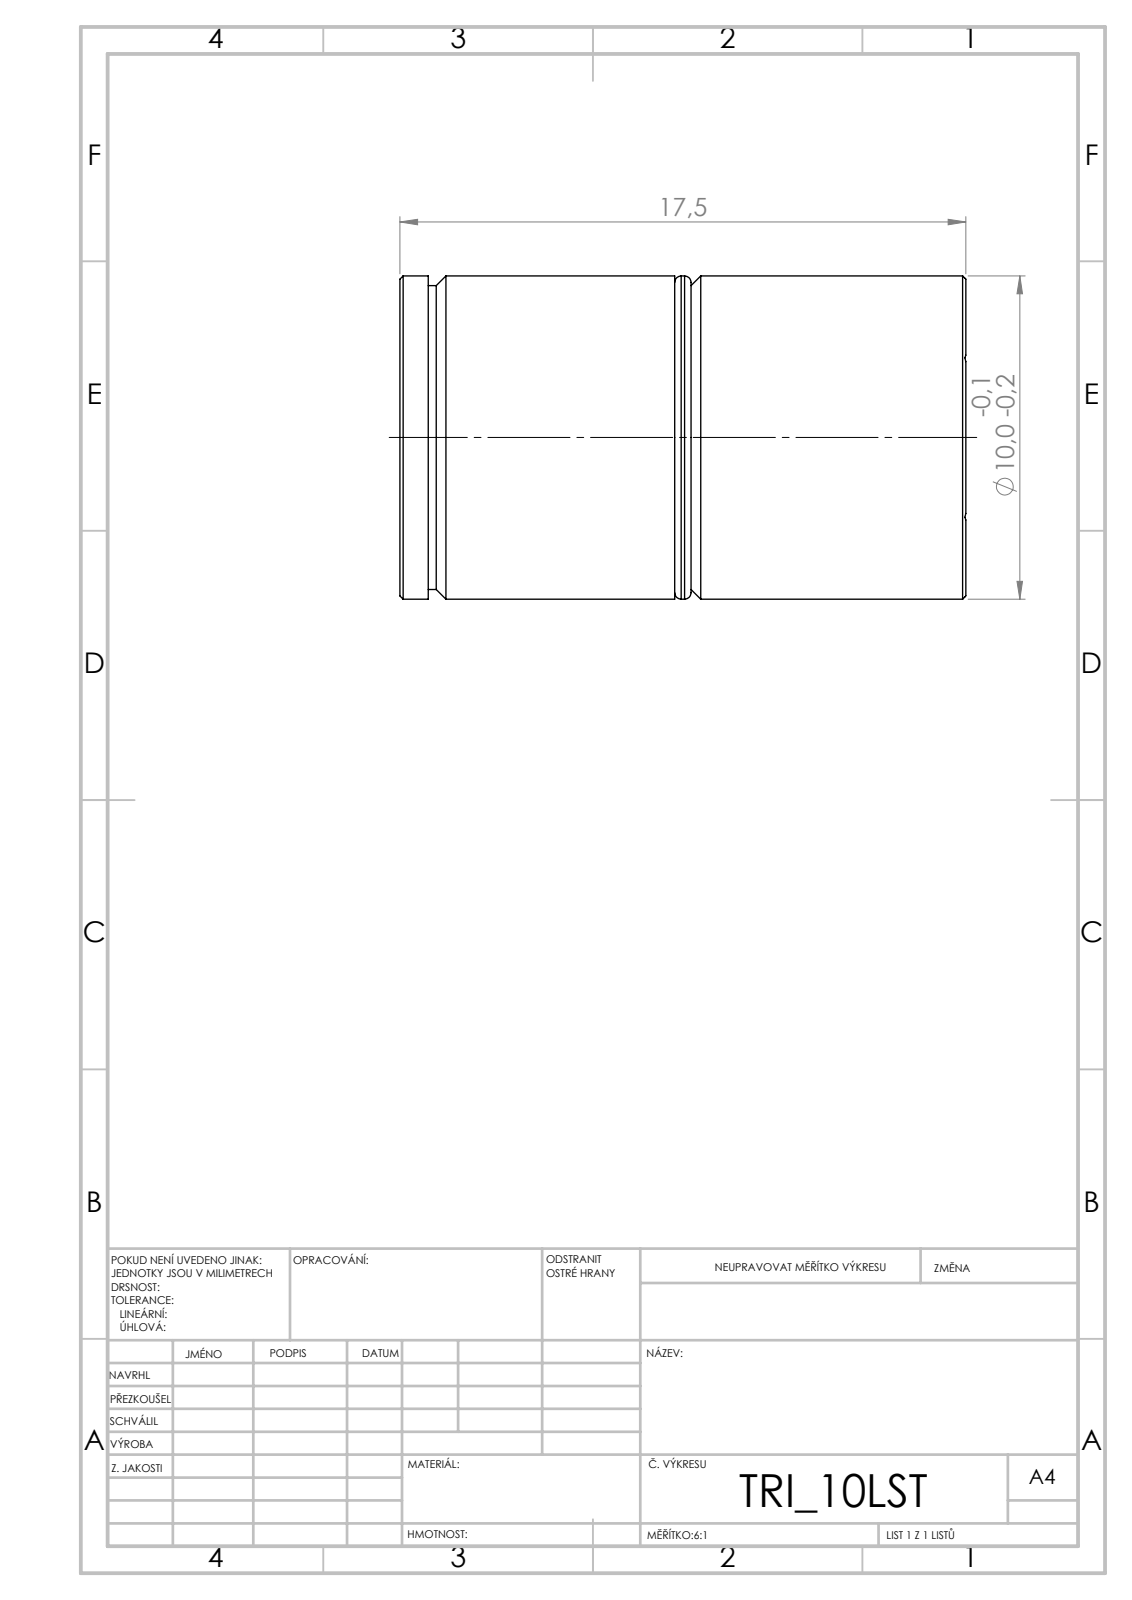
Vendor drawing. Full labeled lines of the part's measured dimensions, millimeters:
STEP written by: SolidWorks 2019 (CONFIG_CONTROL_DESIGN)
Units: millimetres
Bodies: 2 solids, 48 faces (24 planar, 12 cylindrical, 12 other)
Overall size (bounding box): 17.5 × 10 × 10
Volume: 1 344 mm³ · Surface area: 920 mm²
Round bosses / shafts (diameter × count): ⌀10 ×1, ⌀9.4 ×1
Main face-to-face distances: 8.5, 9, 0.5, 7.5, 8, 16.5, 1, 17.5, 8.2, 16.63
